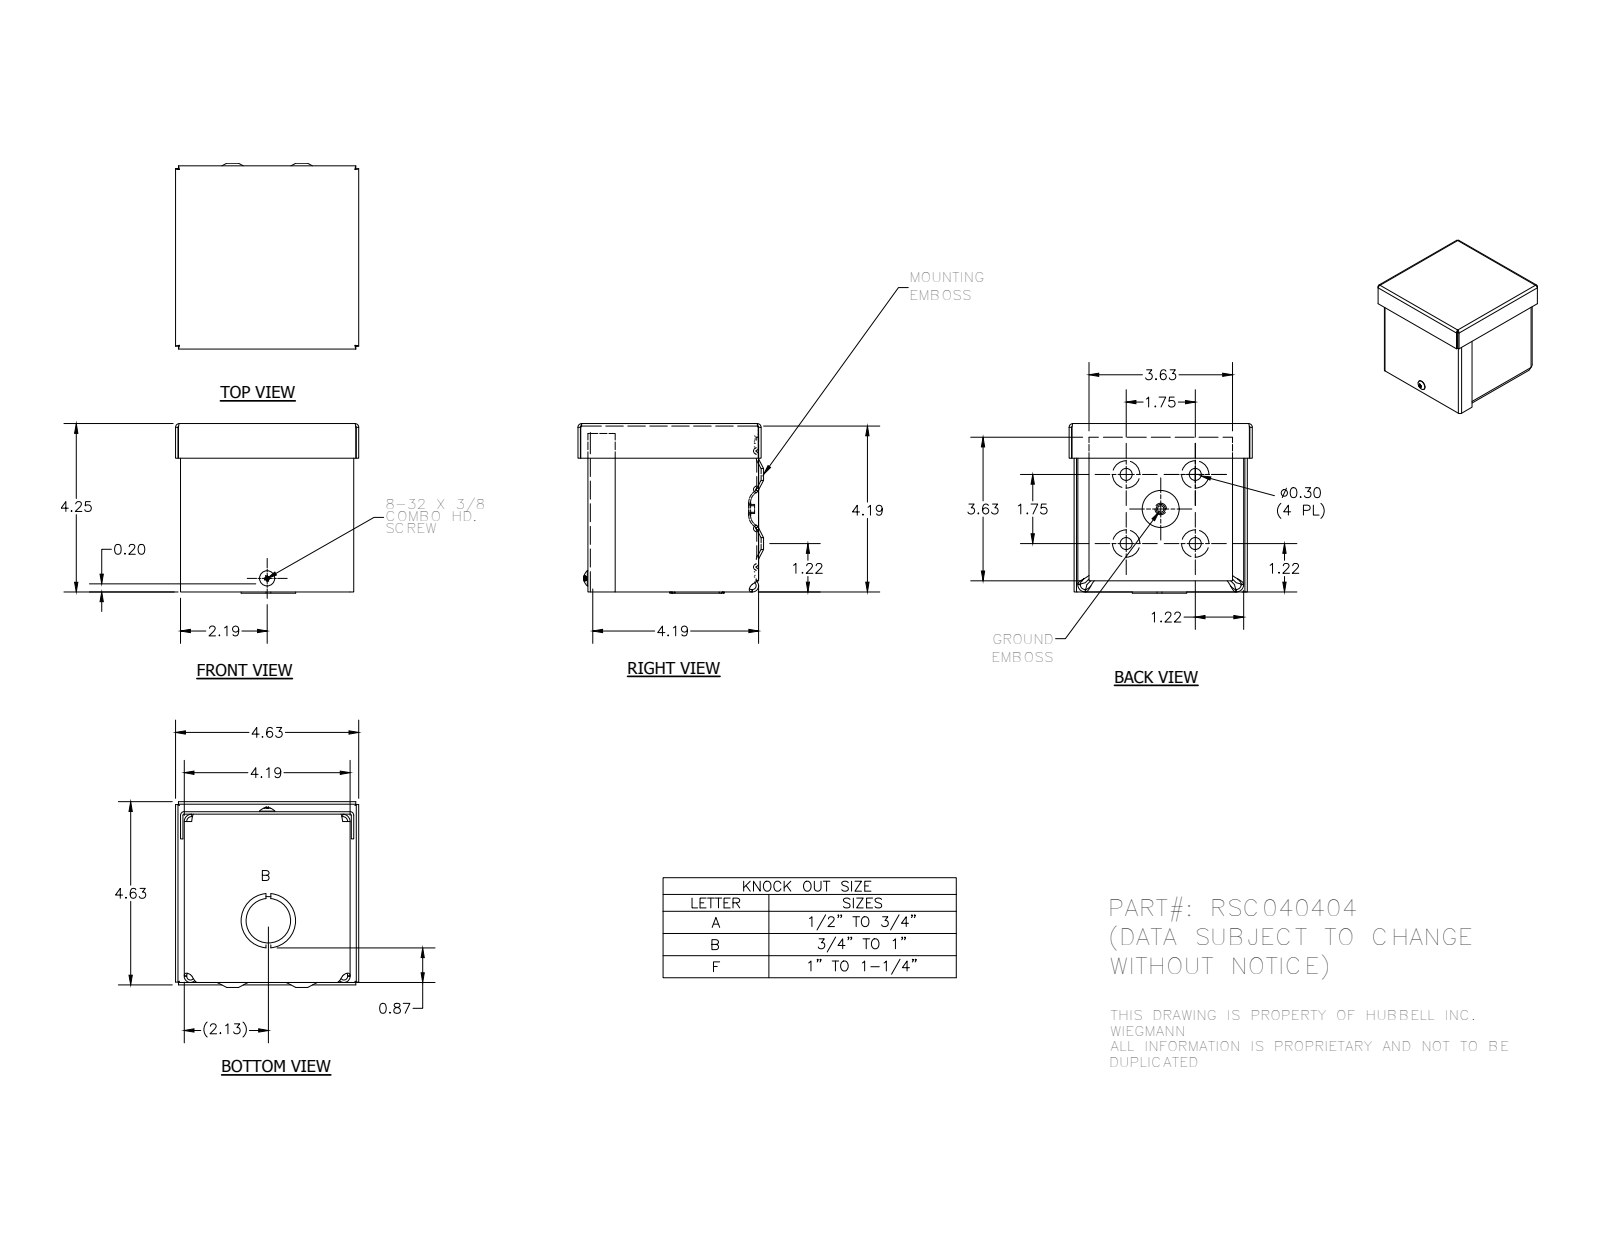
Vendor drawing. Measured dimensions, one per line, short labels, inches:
name: RSC040404; RSC040404_WRAP; RSC0404_LID; RSC0404_CAP (+3 more)
written by: Autodesk Inventor 2012 (AUTOMOTIVE_DESIGN)
unit: in
bodies: 5 solids, 358 faces (155 planar, 78 cylindrical, 125 other)
size: 4.689 × 4.625 × 4.281
volume: 9.837 in³; area: 325.3 in²
holes: 4× ⌀0.3, 2× ⌀0.313, 1× ⌀0.148, 1× ⌀0.165, 1× ⌀1.125, 1× ⌀1.375
bosses: 1× ⌀0.384, 1× ⌀0.229, 1× ⌀0.164
rounds: 8× R0.125, 8× R0.187, 6× R0.031, 6× R0.093, 4× R0.01, 4× R0.055, 4× R0.062, 4× R0.094
face distances: 0.062, 4.126, 0.062, 4.188, 0.124, 4.25, 4.187, 4.249, 4.063, 4.187
hole spacings: 1.234, 1.234, 1.745, 1.745, 2.468, 1.111, 1.112, 1.237
